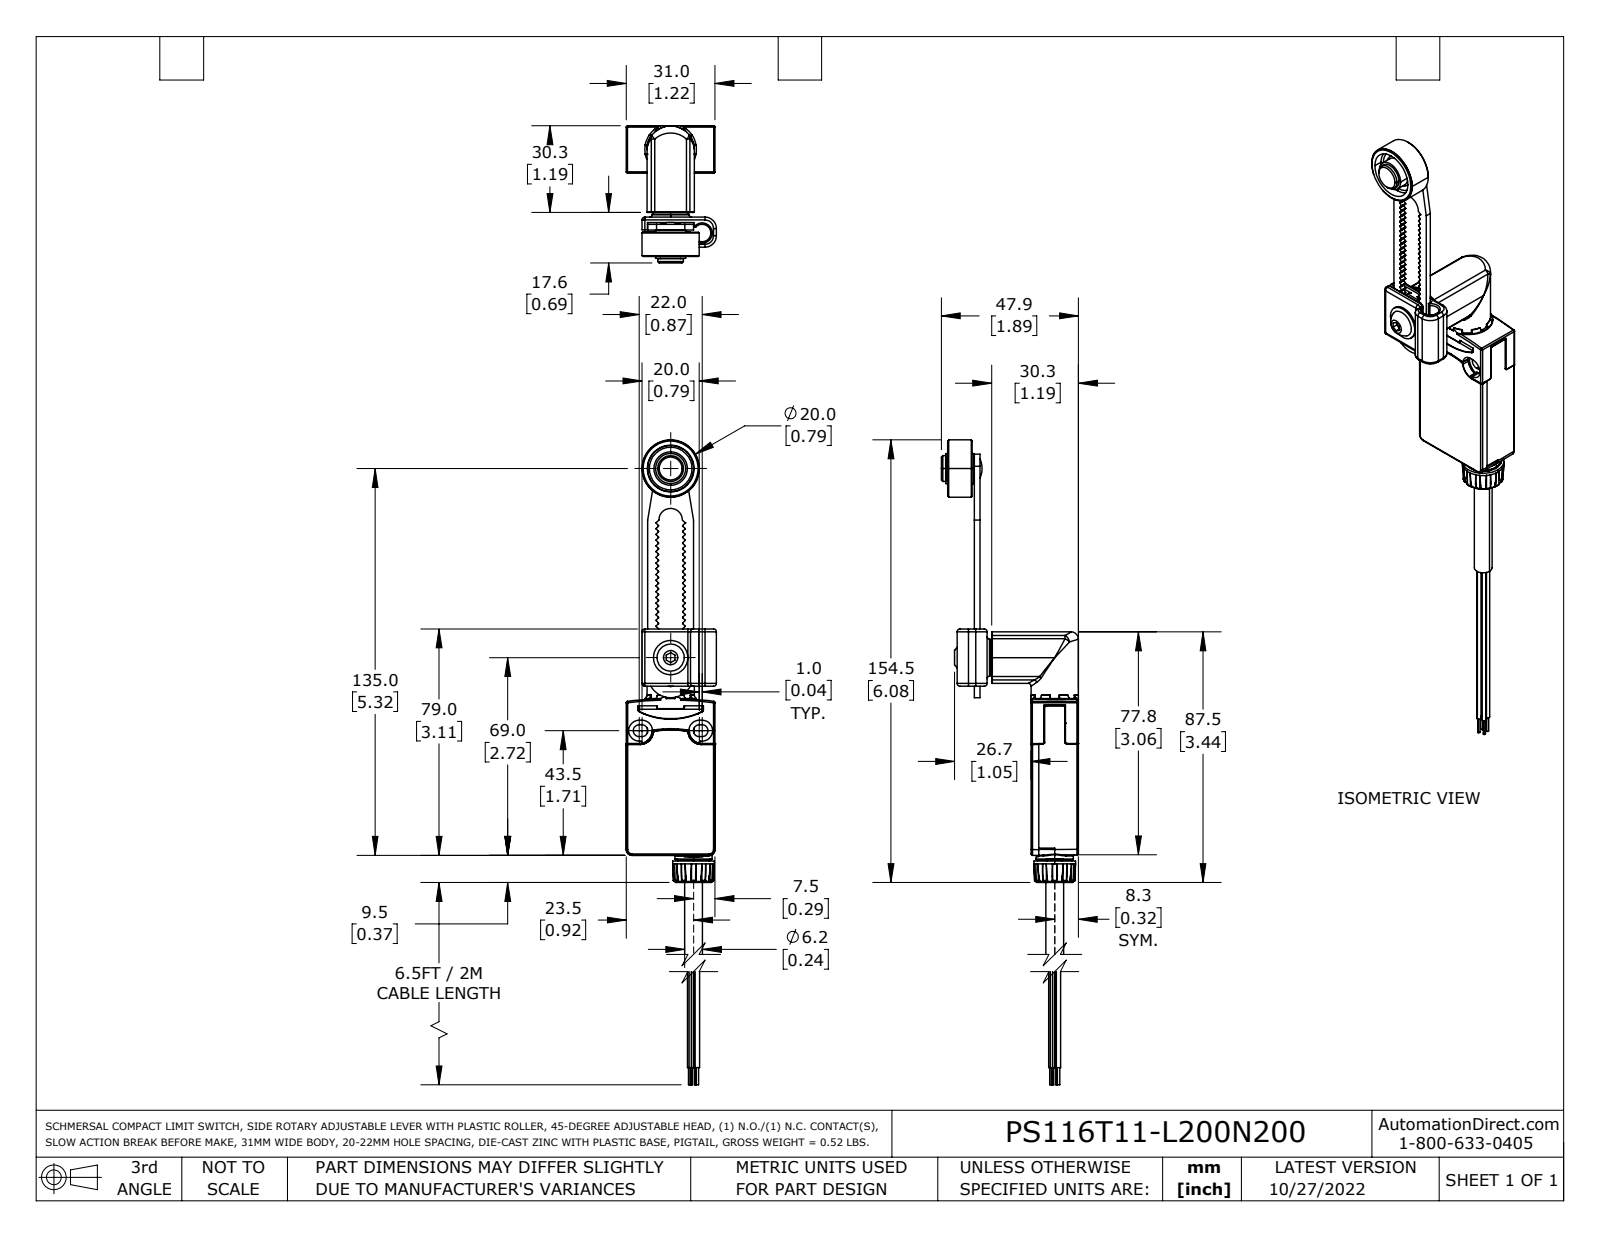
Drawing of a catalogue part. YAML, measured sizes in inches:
part_name: "PS116T11-L200N200_Default"
step_written_by: "SolidWorks 2021 (CONFIG_CONTROL_DESIGN)"
units: inches
bodies: {solids: 1, faces: 1556, planar: 489, cylindrical: 714, other: 353}
overall_size: [10.335, 1.886, 1.24]
volume: 2.699
surface_area: 34.77
round_holes:
  - {diameter: 0.48, count: 2}
  - {diameter: 0.079, count: 1}
  - {diameter: 0.24, count: 1}
  - {diameter: 0.252, count: 1}
  - {diameter: 0.315, count: 1}
  - {diameter: 0.571, count: 1}
  - {diameter: 0.583, count: 1}
round_bosses_or_shafts:
  - {diameter: 0.059, count: 4}
  - {diameter: 0.031, count: 4}
  - {diameter: 0.512, count: 2}
  - {diameter: 0.787, count: 1}
  - {diameter: 0.65, count: 1}
  - {diameter: 0.571, count: 1}
  - {diameter: 0.567, count: 1}
  - {diameter: 0.524, count: 1}
partial_cylinders:
  - {radius: 0.008, count: 253}
  - {radius: 0.004, count: 61}
  - {radius: 0.02, count: 37}
  - {radius: 0.039, count: 27}
  - {radius: 0.079, count: 12}
  - {radius: 0.014, count: 10}
  - {radius: 0.012, count: 6}
  - {radius: 0.118, count: 5}
face_to_face_distances: [0.65, 0.781, 0.079, 1.431, 1.352, 0.703, 0.652, 0.098, 0.177, 0.201]
hole_center_spacings: [0.315, 1.154, 1.227, 2.598]
